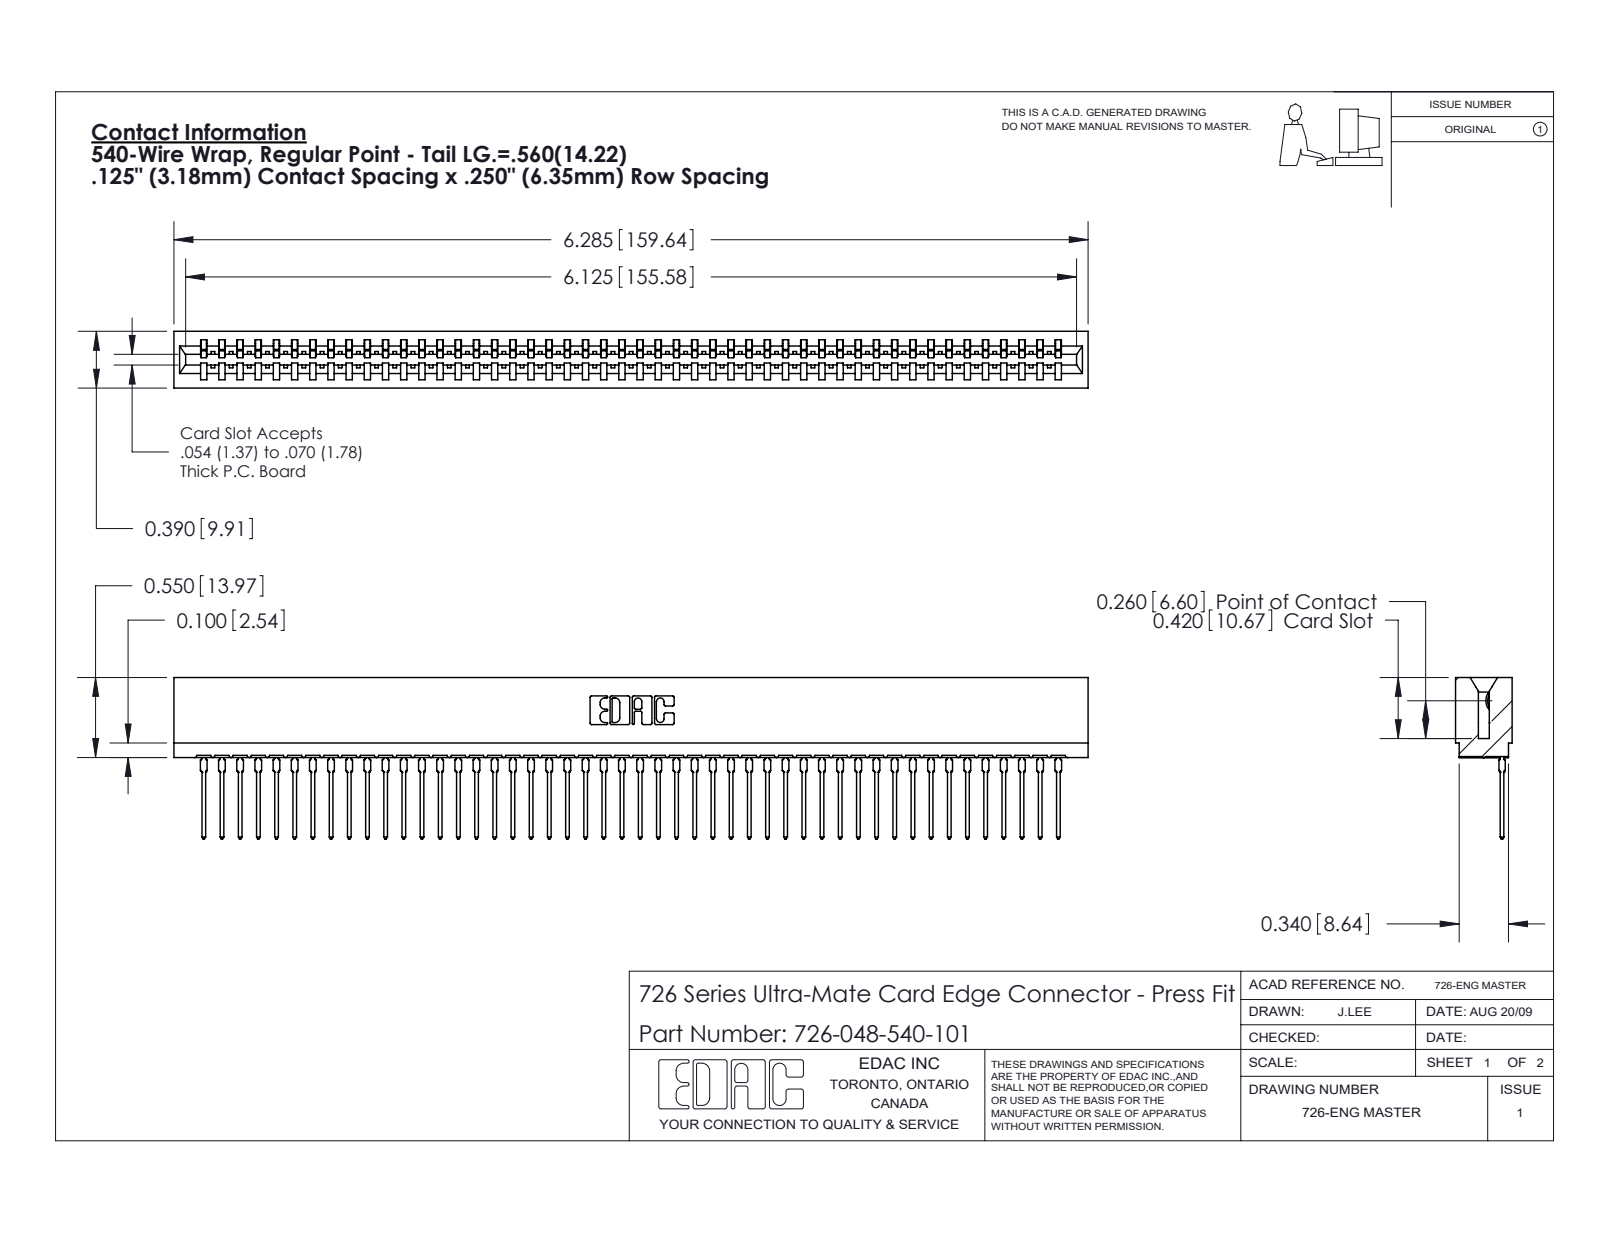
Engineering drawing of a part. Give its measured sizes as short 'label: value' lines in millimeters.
name: 726-048-540-101; 746-292-001_540; 726 Part_.515 Slot Depth - 01
written by: SolidWorks 2020 (CONFIG_CONTROL_DESIGN)
unit: mm
bodies: 49 solids, 5281 faces (3079 planar, 954 cylindrical, 1248 other)
size: 159.6 × 28.2 × 9.9
volume: 14 300 mm³; area: 22 540 mm²
rounds: 96× R0.5, 49× R0.4, 22× R0.3, 6× R0.2, 6× R0.8, 4× R0.1, 4× R0.3, 3× R0.7
face distances: 1.4, 8.5, 9.9, 0.6, 7.8, 6.4, 2.1, 7, 9.3, 0.8
